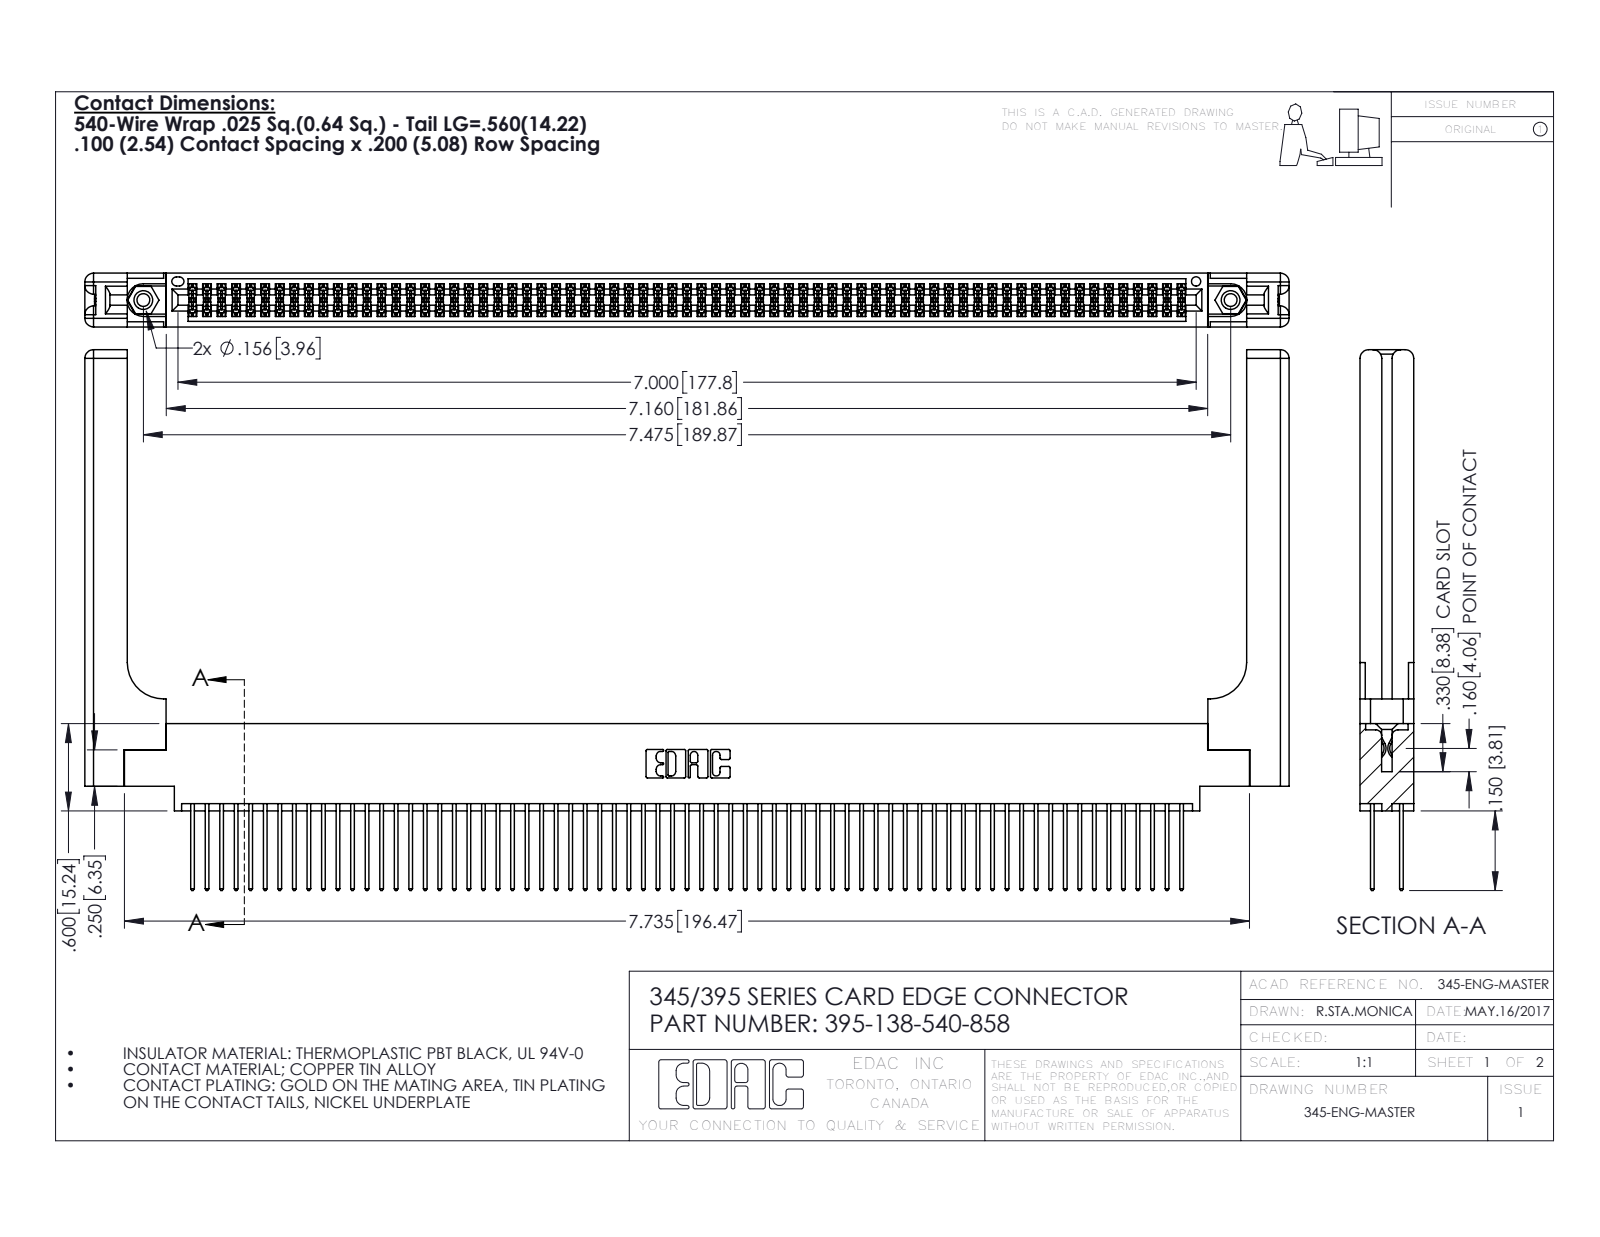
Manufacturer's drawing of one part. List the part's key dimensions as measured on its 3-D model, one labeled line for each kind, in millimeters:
Part name (STEP PRODUCT): 345-220-058_345-220-058; 345-292-001_345-293-140; 395-138-540-858; 345-250-001_345-250-001-102 (+1 more)
STEP written by: SolidWorks 2016 (CONFIG_CONTROL_DESIGN)
Units: millimetres
Bodies: 143 solids, 7286 faces (4786 planar, 2440 cylindrical, 60 other)
Overall size (bounding box): 210.3 × 94.4 × 9.4
Volume: 29 560 mm³ · Surface area: 39 320 mm²
Round holes (diameter × count): ⌀2.3 ×2, ⌀3.2 ×2, ⌀4 ×2, ⌀1.6 ×1
Round bosses / shafts (diameter × count): ⌀3.9 ×2
Partial cylindrical surfaces — rounded edges, fillets, slot ends (radius × count): R0.2 ×207, R0.3 ×138, R0.3 ×22, R1.5 ×16, R0.2 ×6, R0.8 ×6, R0.7 ×3, R0.4 ×2
Main face-to-face distances: 1.8, 7.6, 9.4, 2.5, 6.9, 0.6, 5.1, 5.7, 4.4, 3.8
Hole centre spacings: 6.9, 183.9, 189.9
